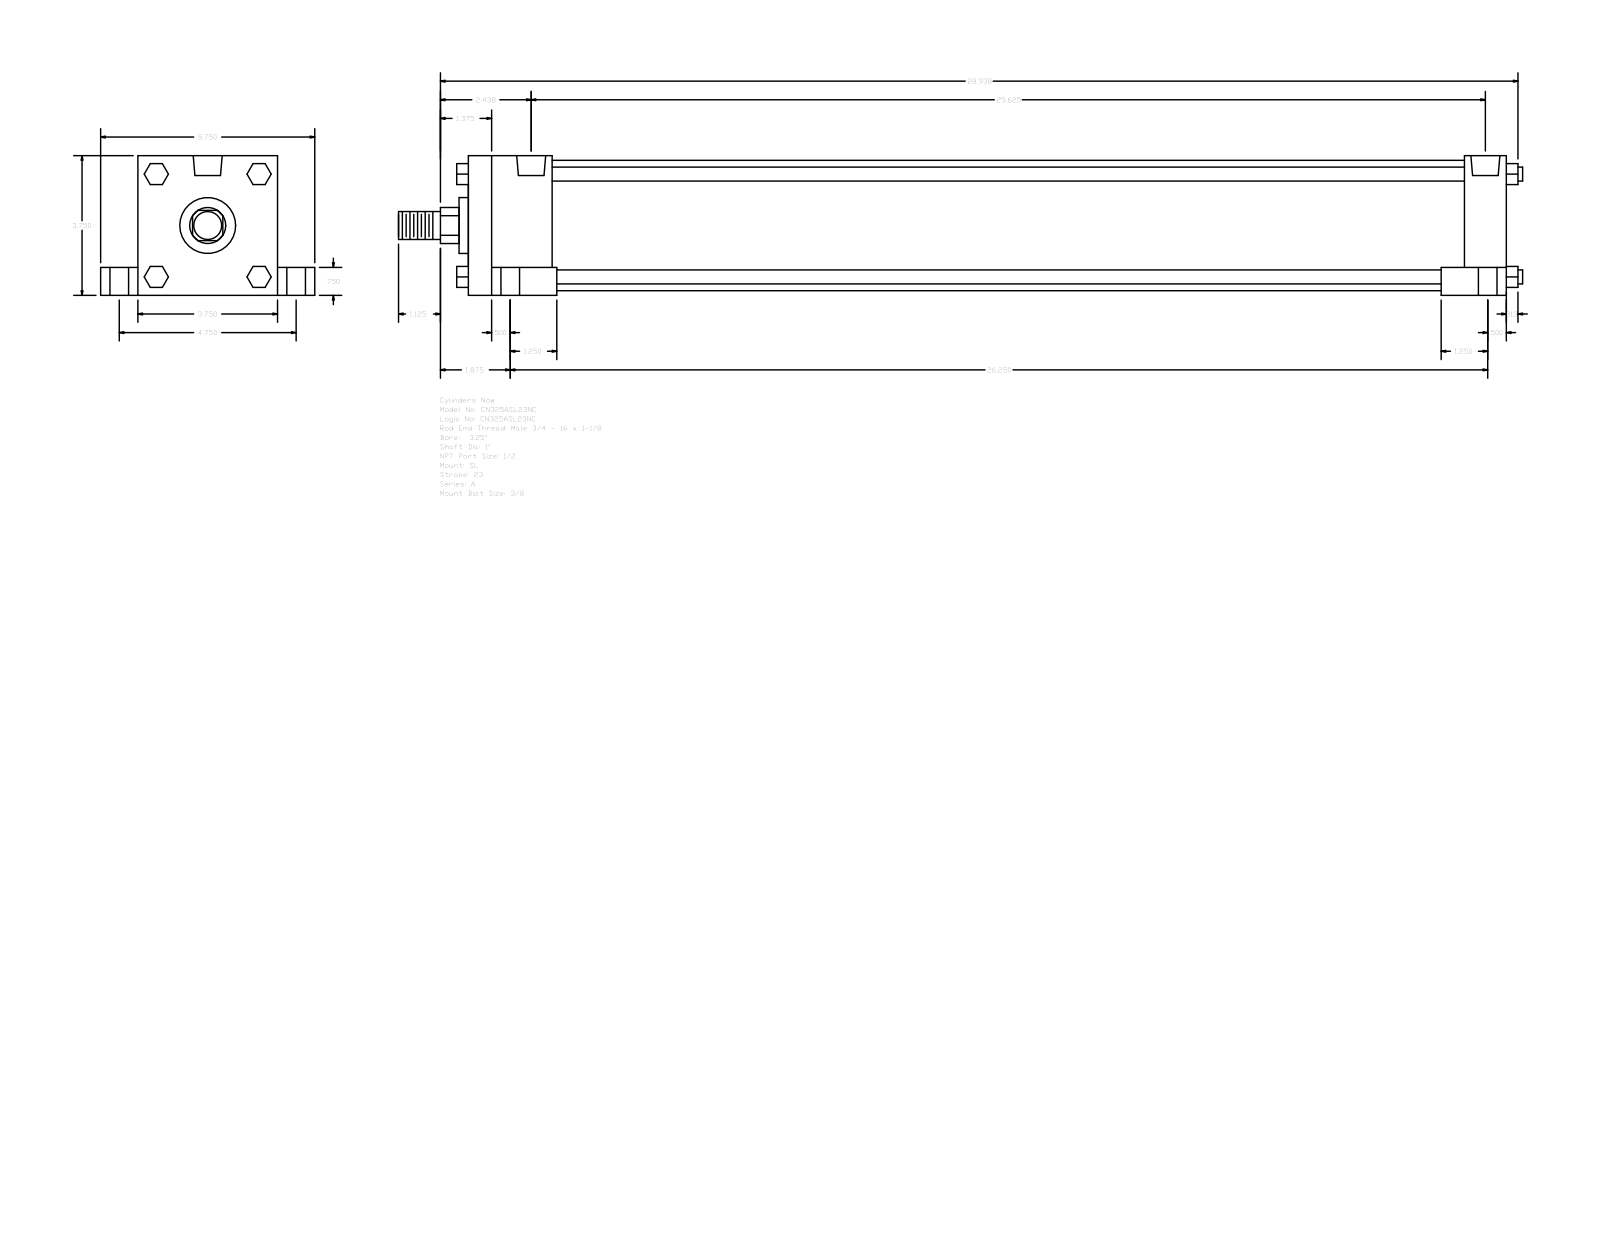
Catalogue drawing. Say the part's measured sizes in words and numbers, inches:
The part is named "A_SL__0325_1". Its 3-D file was written by "GSSL Pune (CONFIG_CONTROL_DESIGN)". It is 0 solids with 150 faces: 114 planar, 36 cylindrical and 0 other. Overall it measures 30.187 by 5.75 by 3.75 inches. Round holes: 4 of diameter 0.344, 4 of diameter 0.5, 4 of diameter 0.75, 2 of diameter 0.778. Round bosses or shafts: 4 of diameter 0.375, 1 of diameter 3.5, 1 of diameter 1.5, 1 of diameter 1, 1 of diameter 0.75. Partial cylindrical surfaces (rounded edges, fillets, slot ends): 1 of radius 0.484. The main face-to-face distances are 3.75, 27.875, 0.75, 1, 4.75, 3, 2.25, 26.75, 24.5, 25.625. The hole center spacings are 0.125, 2.376, 2.383, 2.441, 2.473, 4.75, 25.375, 25.5.
